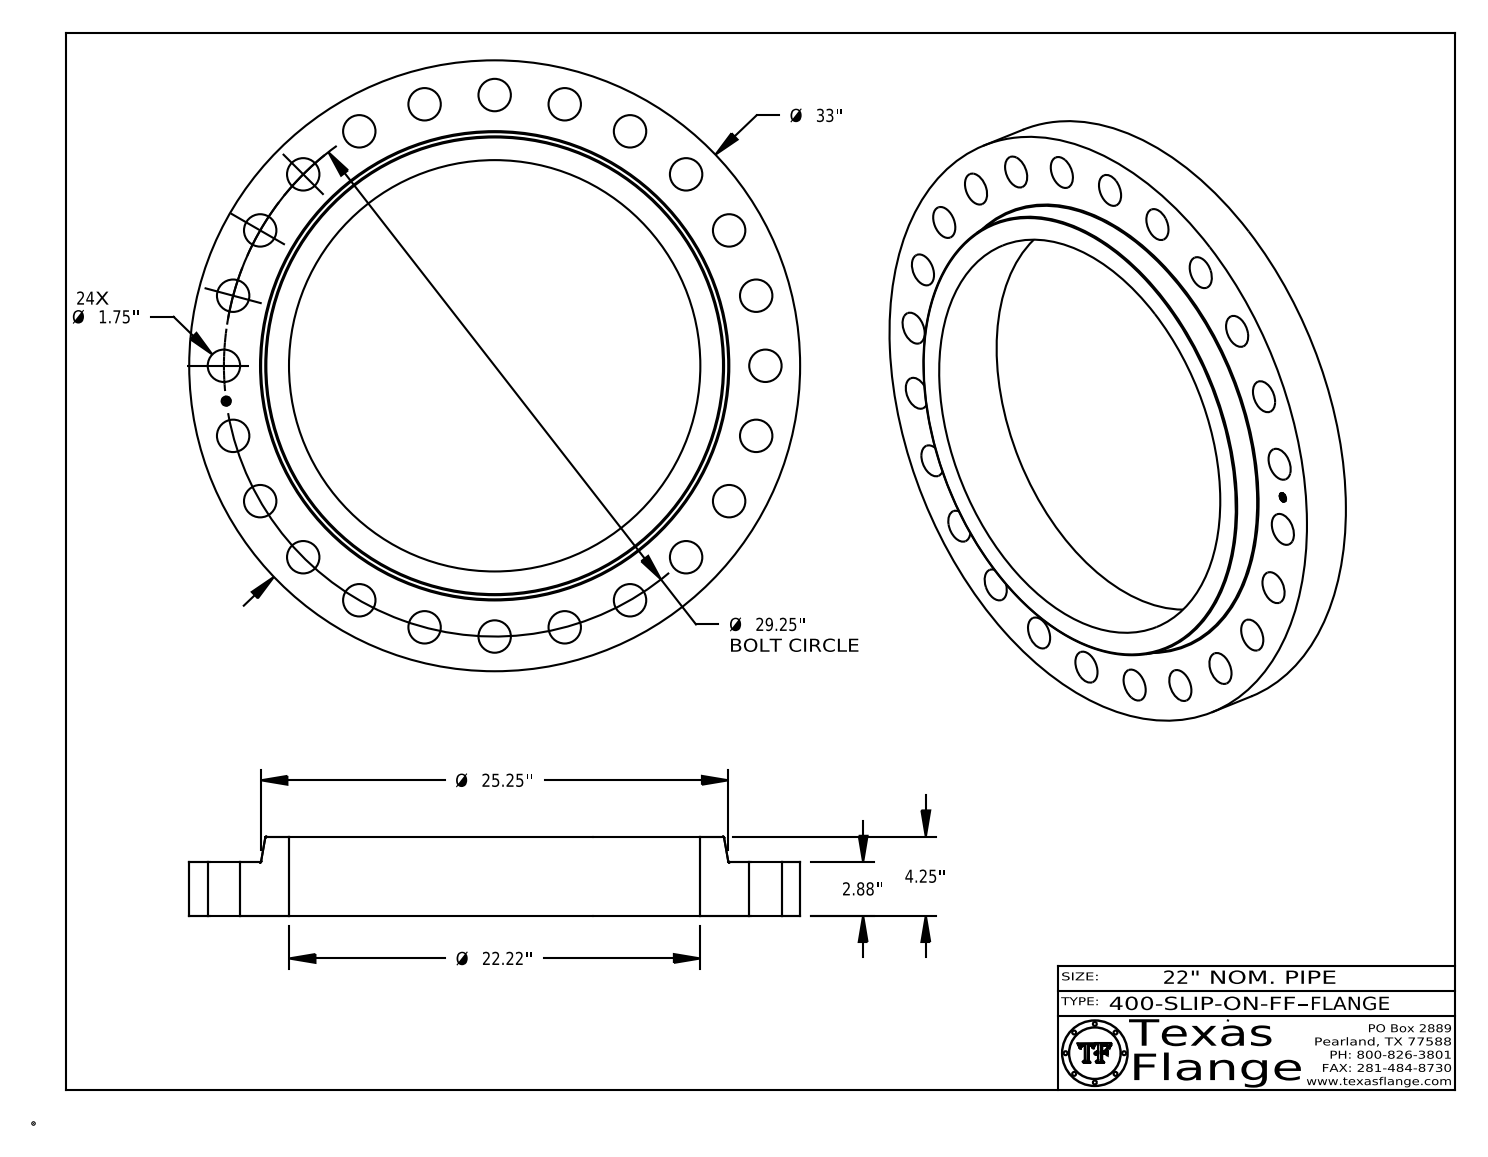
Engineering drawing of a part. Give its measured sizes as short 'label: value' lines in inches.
name: 400-SLIP-ON-FF
written by: CATIA V5 STEP AP214 (AUTOMOTIVE_DESIGN)
unit: in
bodies: 1 solid, 446 faces (368 planar, 72 cylindrical, 6 other)
size: 33 × 33 × 4.25
volume: 1 322 in³; area: 1 883 in²
holes: 24× ⌀1.75, 1× ⌀0.495, 1× ⌀22.22
bosses: 8× ⌀0.03, 1× ⌀33, 1× ⌀0.39
face distances: 2.88, 4.25, 1.37, 2.865, 0.015, 1.385, 0.148, 0.145, 0.027, 0.096
hole spacings: 14.625, 27.024, 7.57, 20.683, 3.818, 11.194, 17.806, 23.206
